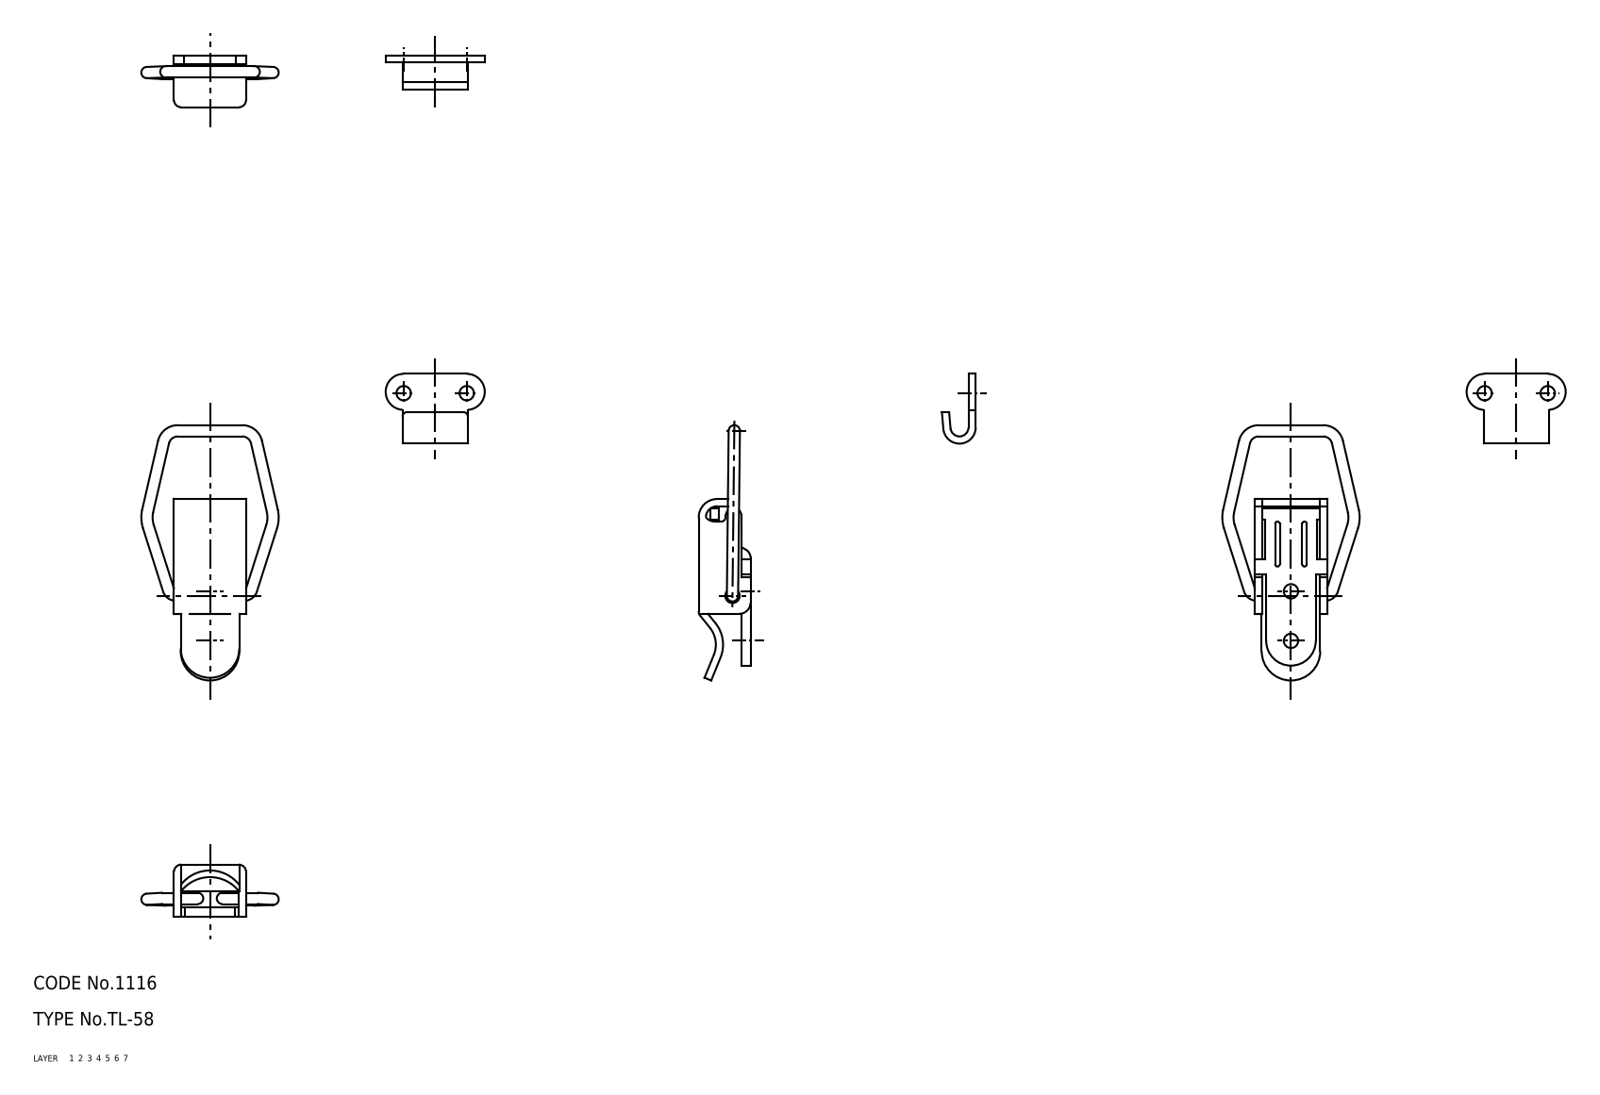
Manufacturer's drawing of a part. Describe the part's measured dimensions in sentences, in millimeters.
The part is named "lever; keeper; base; arm (+1 more)". Its 3-D file was written by "CADfix (AUTOMOTIVE_DESIGN)". It is 4 solids with 133 faces: 0 planar, 0 cylindrical and 133 other. Overall it measures 68.09 by 30.48 by 11.5 millimeters. Its volume is 3 591 cubic millimeters and its surface area 5 183 square millimeters.
